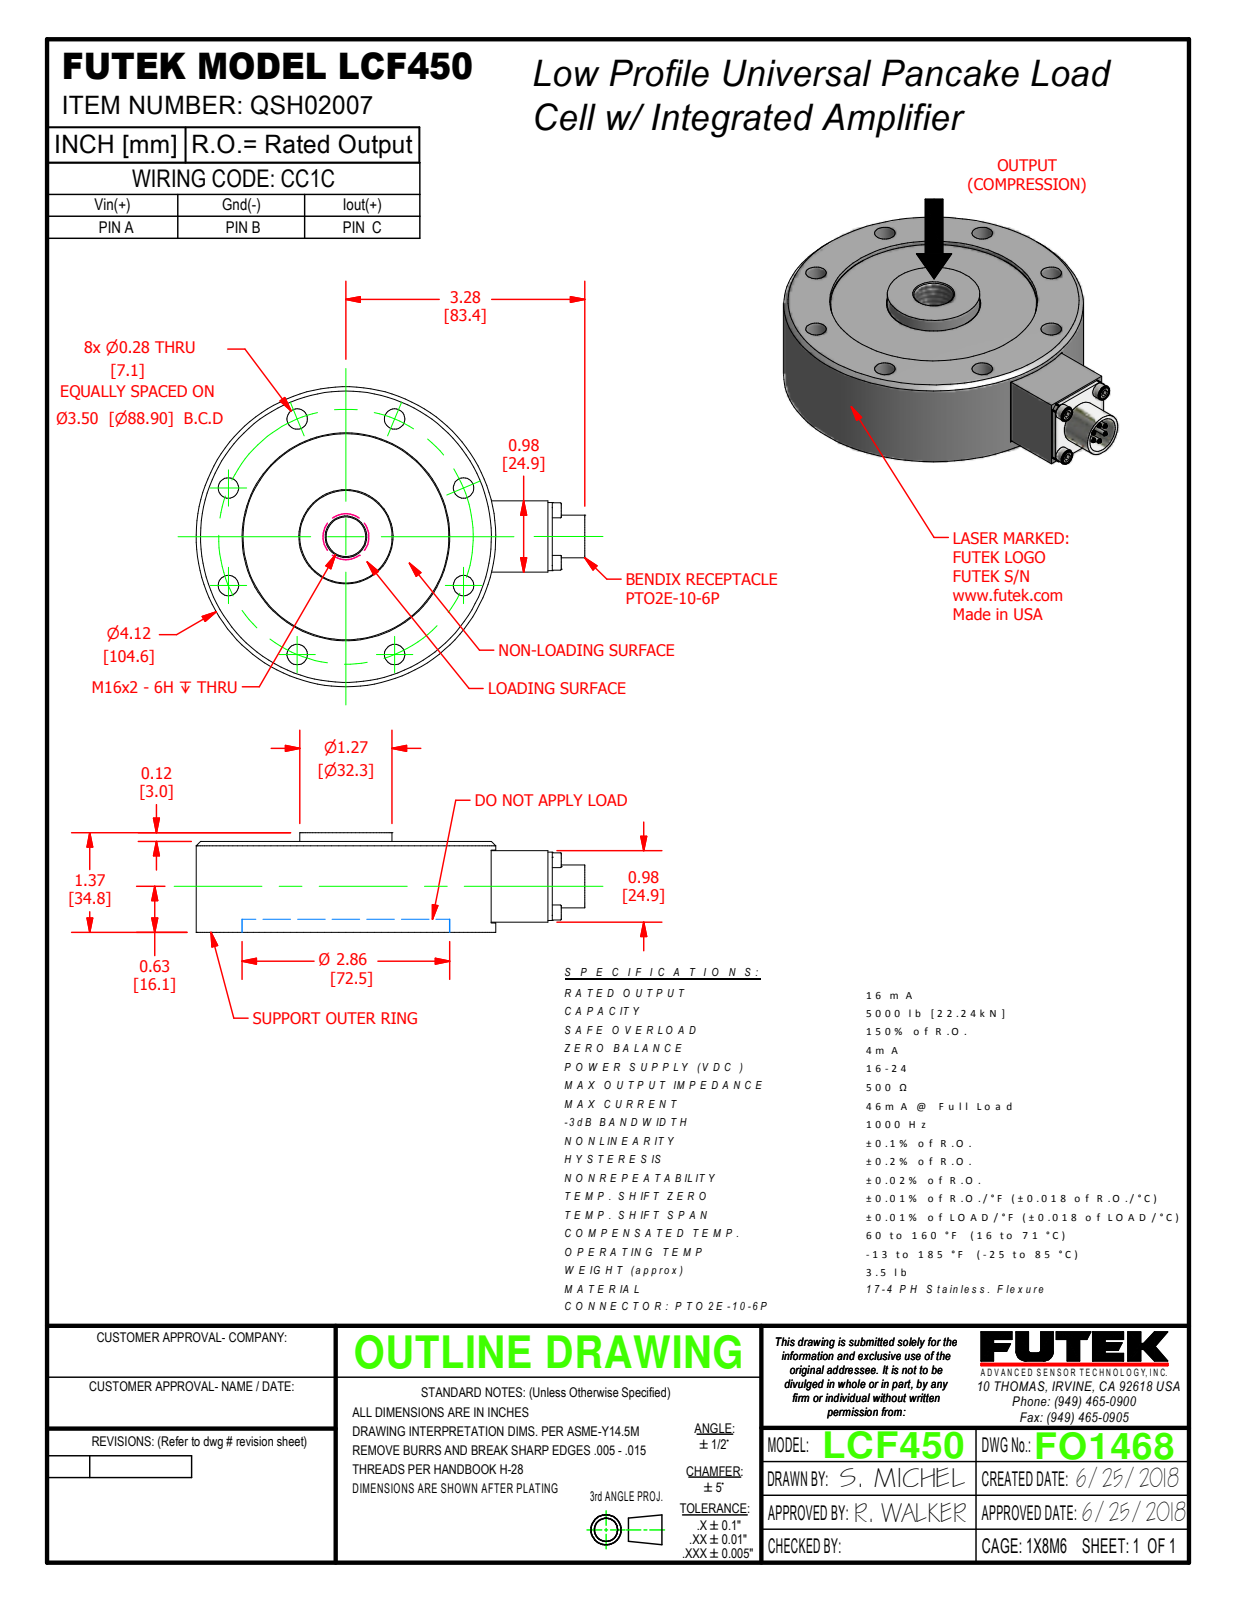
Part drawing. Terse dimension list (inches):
name: Assembly2_Shrinkwrap_1
written by: Autodesk Inventor 2018 (AUTOMOTIVE_DESIGN)
unit: in
bodies: 1 solid, 125 faces (66 planar, 41 cylindrical, 18 other)
size: 5.344 × 4.12 × 1.37
volume: 15.78 in³; area: 62.74 in²
holes: 8× ⌀0.281, 1× ⌀0.492, 1× ⌀0.545, 1× ⌀1.295, 1× ⌀2.855, 1× ⌀4
bosses: 6× ⌀0.06, 4× ⌀0.205, 1× ⌀4.12, 1× ⌀3, 1× ⌀2.83, 1× ⌀1.27, 1× ⌀0.587
rounds: 8× R0.01
face distances: 1.22, 0.06, 0.048, 1.172, 1.16, 1.112, 1.25, 1.202, 0.09, 0.03
hole spacings: 3.233, 1.339, 1.75, 2.475, 3.5, 1.75, 1.339, 1.34
